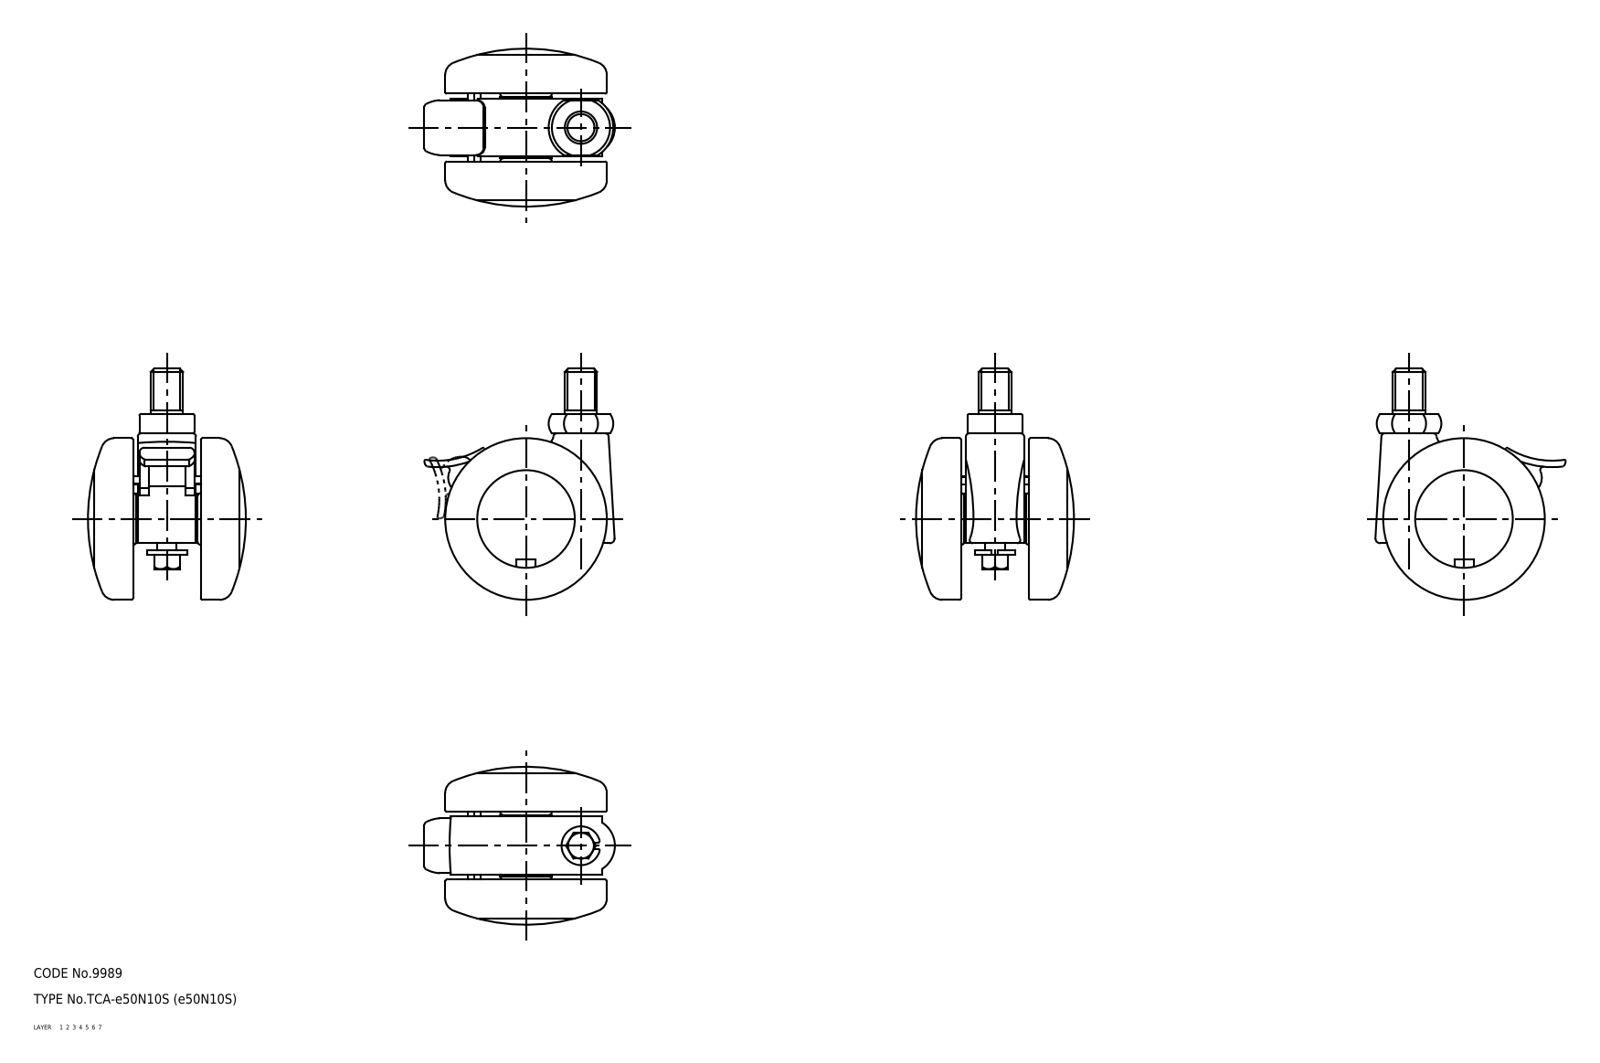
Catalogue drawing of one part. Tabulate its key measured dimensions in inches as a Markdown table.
| quantity | value |
| --- | --- |
| part name | lever; wheel_mr; wheel; main shaft (+1 more) |
| STEP written by | CADfix (AUTOMOTIVE_DESIGN) |
| units | inches |
| bodies | 5 solids, 211 faces (0 planar, 0 cylindrical, 211 other) |
| overall size | 2.815 × 2.317 × 1.924 |
| volume | 3.848 in³ |
| surface area | 41.94 in² |
